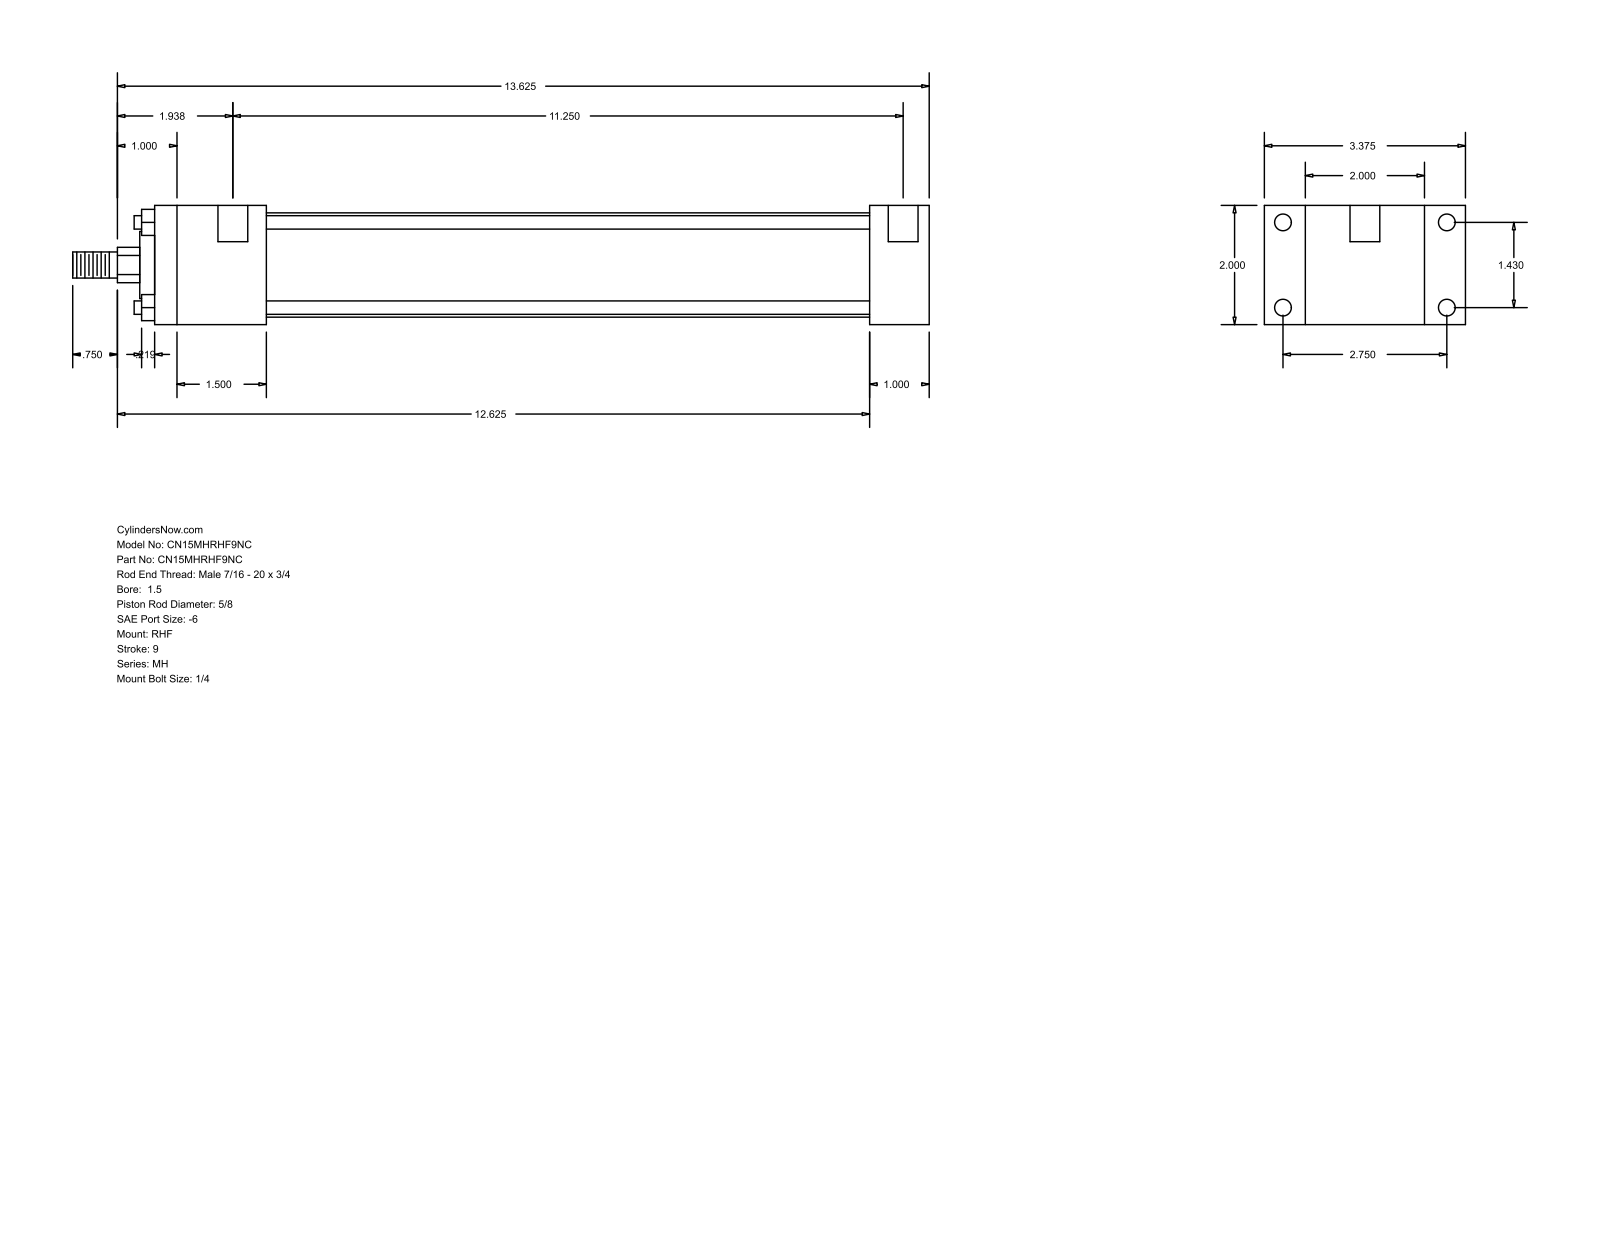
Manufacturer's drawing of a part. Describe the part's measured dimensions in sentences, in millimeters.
The part is named "MH_RHF__0150_0.625". Its 3-D file was written by "GSSL Pune (CONFIG_CONTROL_DESIGN)". It is 0 solids with 88 faces: 60 planar, 28 cylindrical and 0 other. Overall it measures 365.12 by 85.72 by 50.8 millimeters. Round holes: 4 of diameter 5.56, 4 of diameter 7.14, 2 of diameter 12.7. Round bosses or shafts: 4 of diameter 5.71, 1 of diameter 44.45, 1 of diameter 28.57, 1 of diameter 15.88, 1 of diameter 11.11. Partial cylindrical surfaces (rounded edges, fillets, slot ends): 1 of radius 7.54. The main face-to-face distances are 50.8, 17.46, 68.26, 25.39, 304.8, 330.19, 85.72, 47.62, 257.18, 282.57. The hole center spacings are 36.32, 69.84, 78.72, 288.92, 3.17, 285.75.
